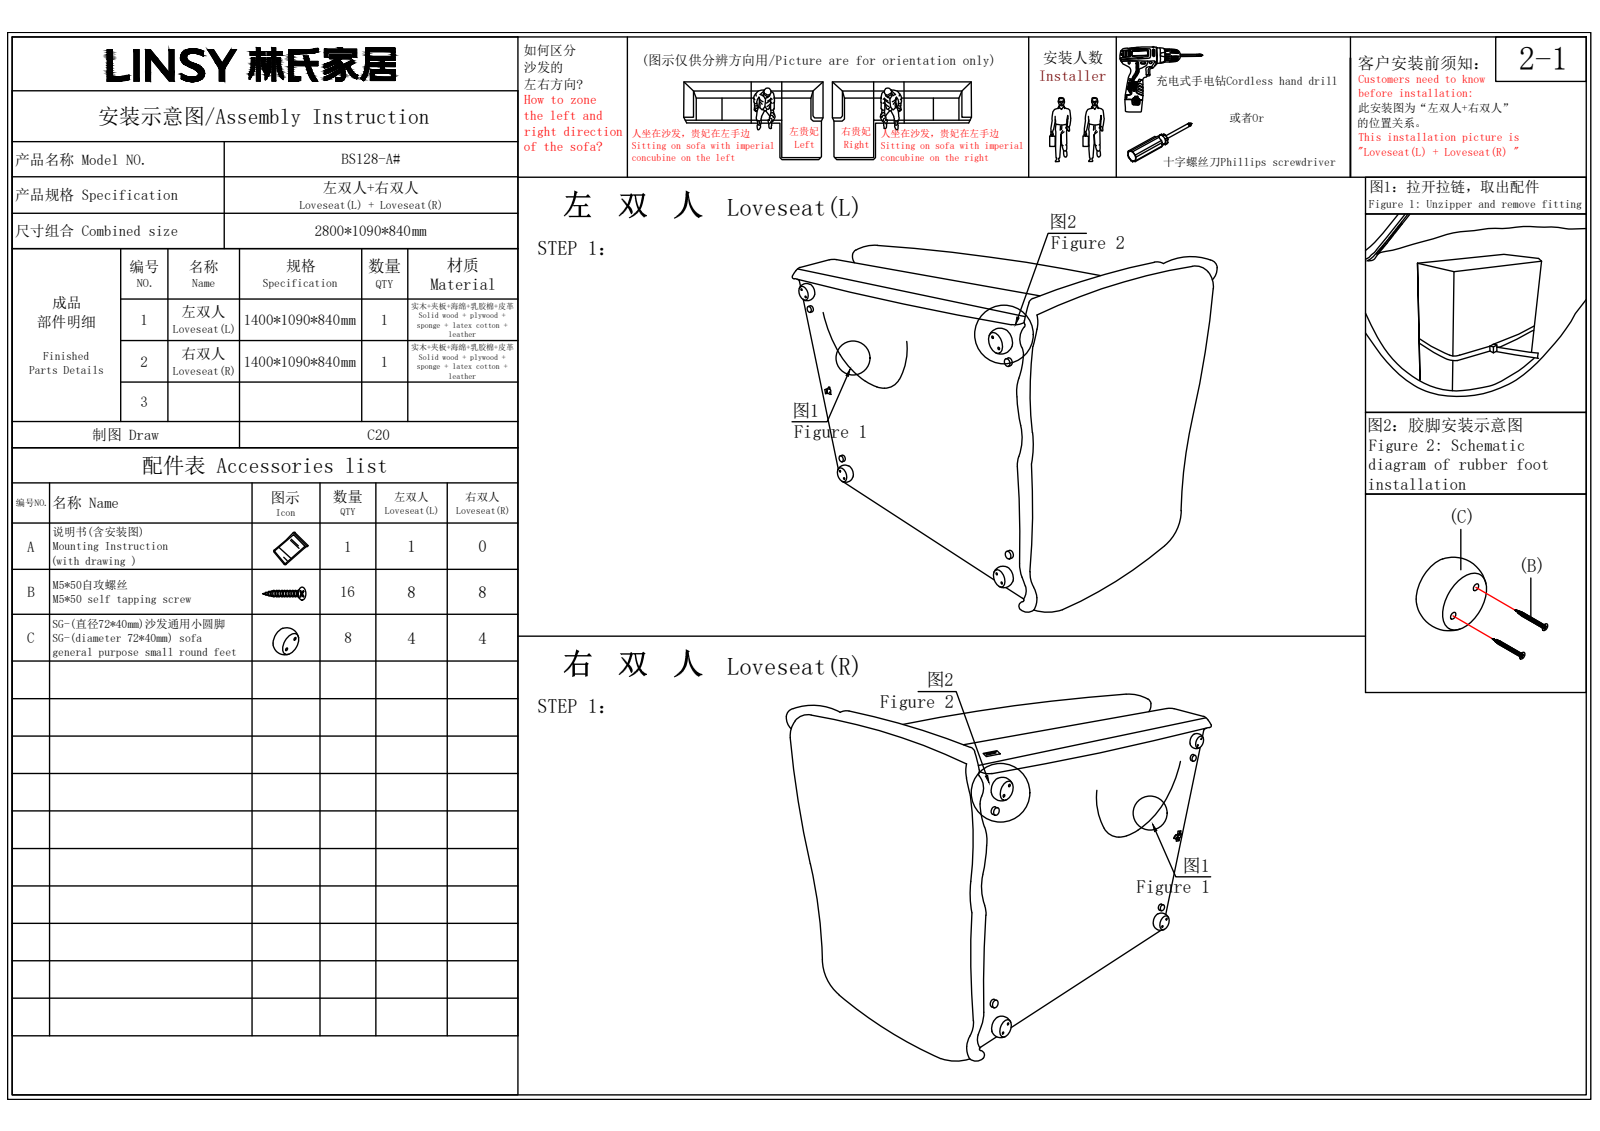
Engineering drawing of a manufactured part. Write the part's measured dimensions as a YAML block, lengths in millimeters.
step_written_by: "ACIS (automotive_design)"
units: millimeters
bodies: {solids: 2, faces: 35, planar: 9, cylindrical: 16, other: 10}
overall_size: [135, 30, 30]
volume: 69440
surface_area: 20099
round_holes:
  - {diameter: 23.59, count: 1}
round_bosses_or_shafts:
  - {diameter: 30, count: 1}
  - {diameter: 23, count: 1}
partial_cylinders:
  - {radius: 1.65, count: 1}
  - {radius: 2.72, count: 1}
  - {radius: 3.75, count: 1}
  - {radius: 11.49, count: 1}
face_to_face_distances: [51, 135, 84, 1.07, 101.02, 50.02, 33.98]
